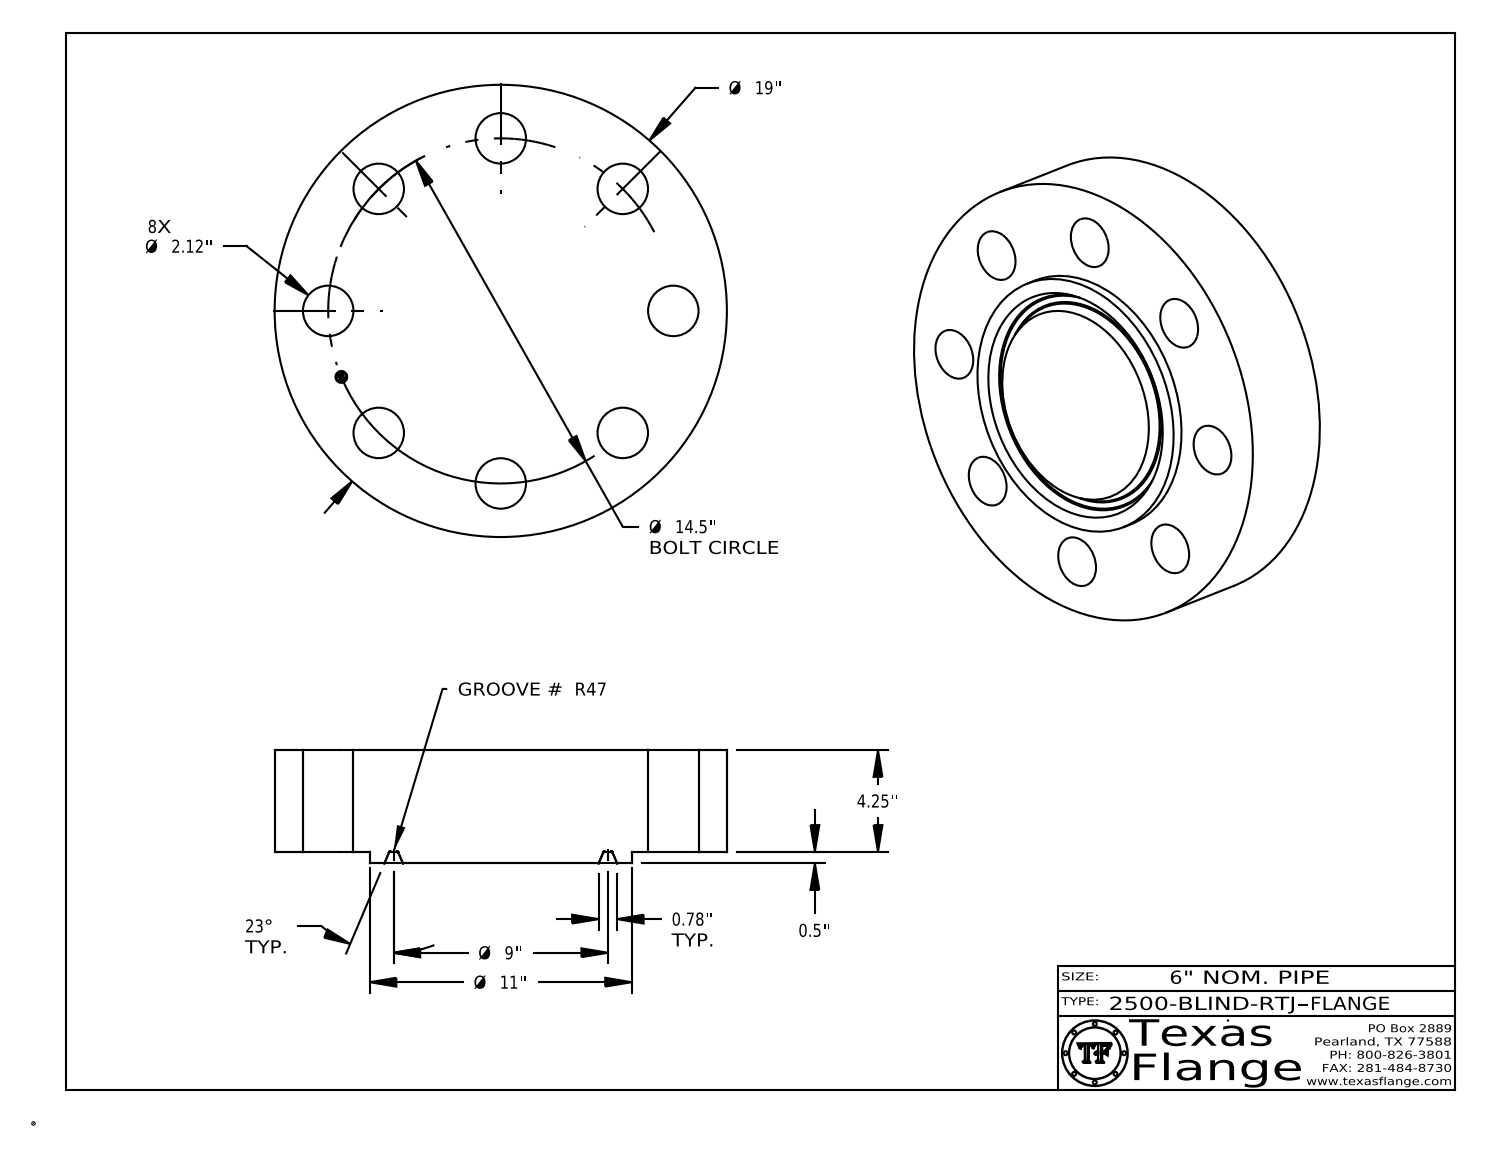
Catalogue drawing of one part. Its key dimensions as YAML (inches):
part_name: "2500-BLIND-RTJ"
step_written_by: "CATIA V5 STEP AP214 (AUTOMOTIVE_DESIGN)"
units: inches
bodies: {solids: 1, faces: 418, planar: 370, cylindrical: 40, other: 8}
overall_size: [19, 19, 4.75]
volume: 1124
surface_area: 1026
round_holes:
  - {diameter: 2.12, count: 8}
  - {diameter: 0.495, count: 1}
round_bosses_or_shafts:
  - {diameter: 0.03, count: 8}
  - {diameter: 19, count: 1}
  - {diameter: 11, count: 1}
  - {diameter: 0.39, count: 1}
face_to_face_distances: [4.25, 0.5, 4.75, 0.015, 4.735, 4.235, 0.148, 0.145, 0.027, 0.096]
hole_center_spacings: [5.549, 13.396, 10.253, 10.253, 2.829, 14.221, 14.5, 14.5]
